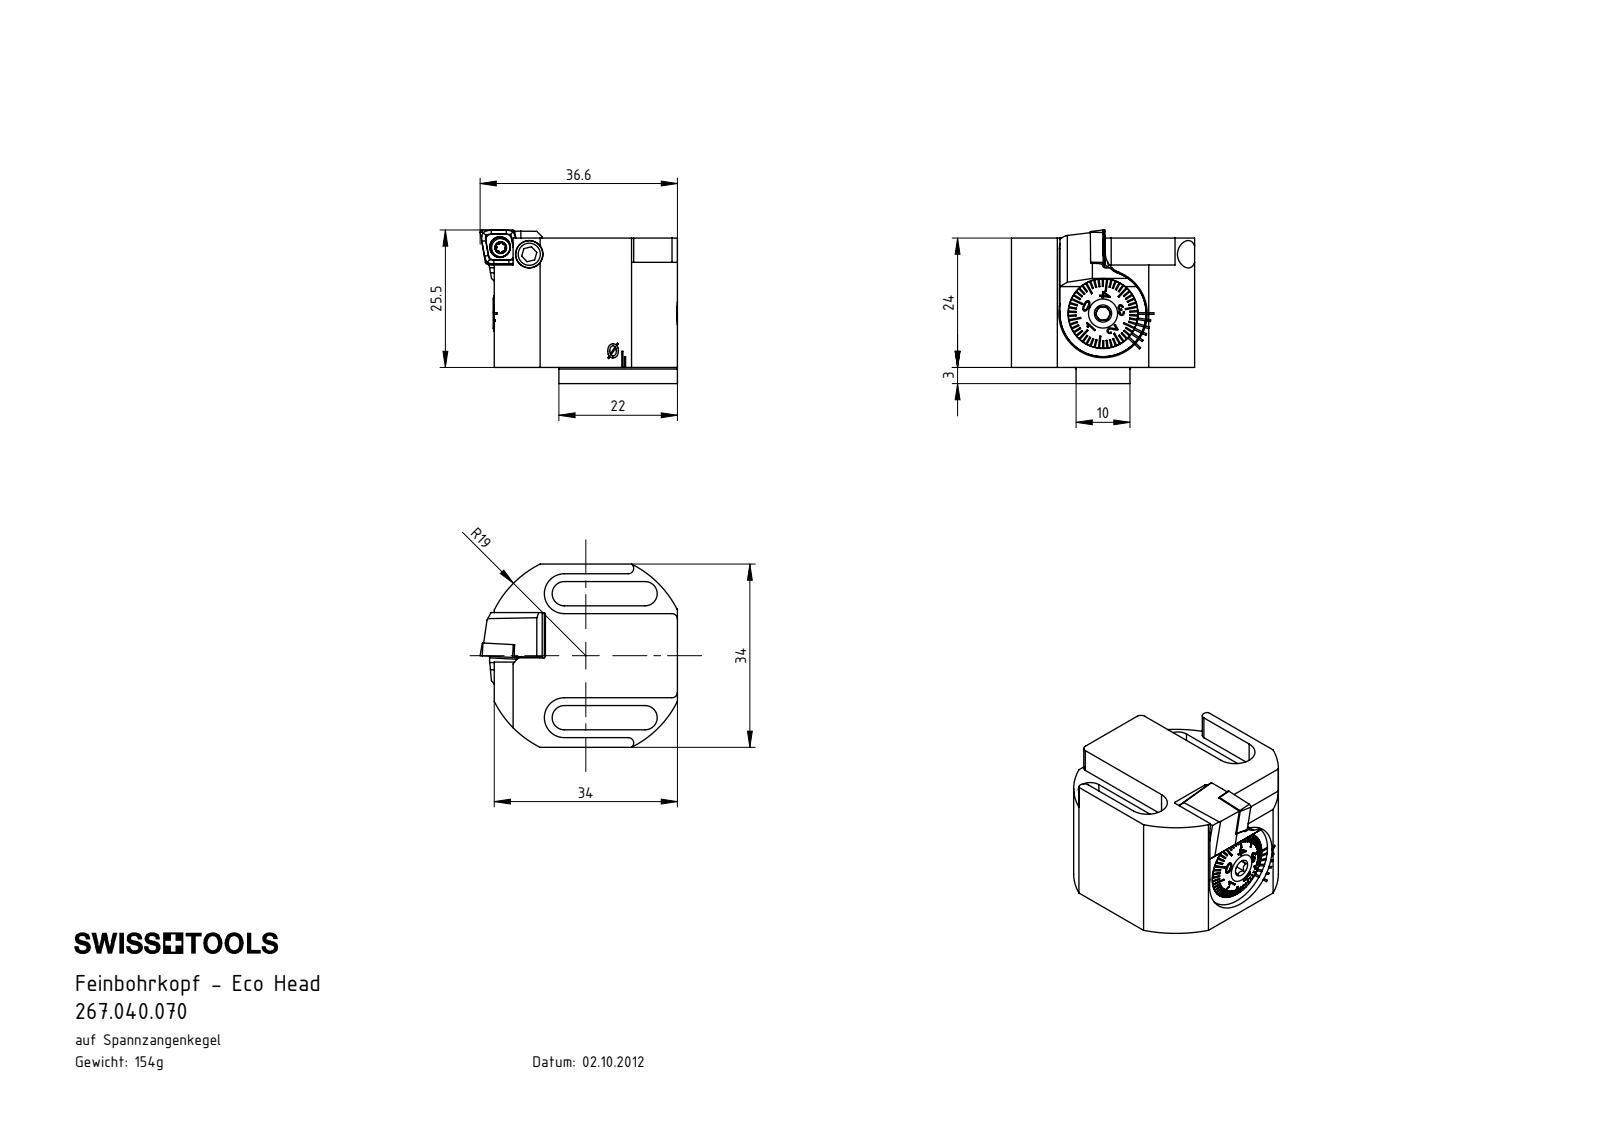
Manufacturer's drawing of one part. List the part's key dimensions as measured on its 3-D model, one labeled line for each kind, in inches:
Part name (STEP PRODUCT): DIN 5401-03; BN 1375 - ø16xø8.2x0.4_vorgespannt; ISO 2338 - 2 h8 x 10; DIN 3771 - 11x1 (+8 more)
STEP written by: SolidWorks 2017 (CONFIG_CONTROL_DESIGN)
Units: inches
Bodies: 26 solids, 617 faces (325 planar, 89 cylindrical, 203 other)
Overall size (bounding box): 1.442 × 1.339 × 1.122
Volume: 1.226 in³ · Surface area: 24.93 in²
Round holes (diameter × count): ⌀0.079 ×1, ⌀0.081 ×1, ⌀0.098 ×1, ⌀0.11 ×1, ⌀0.152 ×1, ⌀0.165 ×1, ⌀0.201 ×1, ⌀0.236 ×1, ⌀0.252 ×1, ⌀0.276 ×1, ⌀0.295 ×1, ⌀0.323 ×1
Round bosses / shafts (diameter × count): ⌀0.685 ×1, ⌀0.646 ×1, ⌀0.643 ×1, ⌀0.63 ×1, ⌀0.516 ×1, ⌀0.506 ×1, ⌀0.441 ×1, ⌀0.272 ×1
Partial cylindrical surfaces — rounded edges, fillets, slot ends (radius × count): R0.008 ×6, R0.012 ×5, R0.014 ×5, R0.039 ×4, R0.089 ×4, R0.02 ×2, R0.146 ×2, R0.014 ×1
Main face-to-face distances: 0.177, 0.906, 0.945, 0.128, 0.305, 1.033, 1.211, 1.339, 0.118, 0.728
